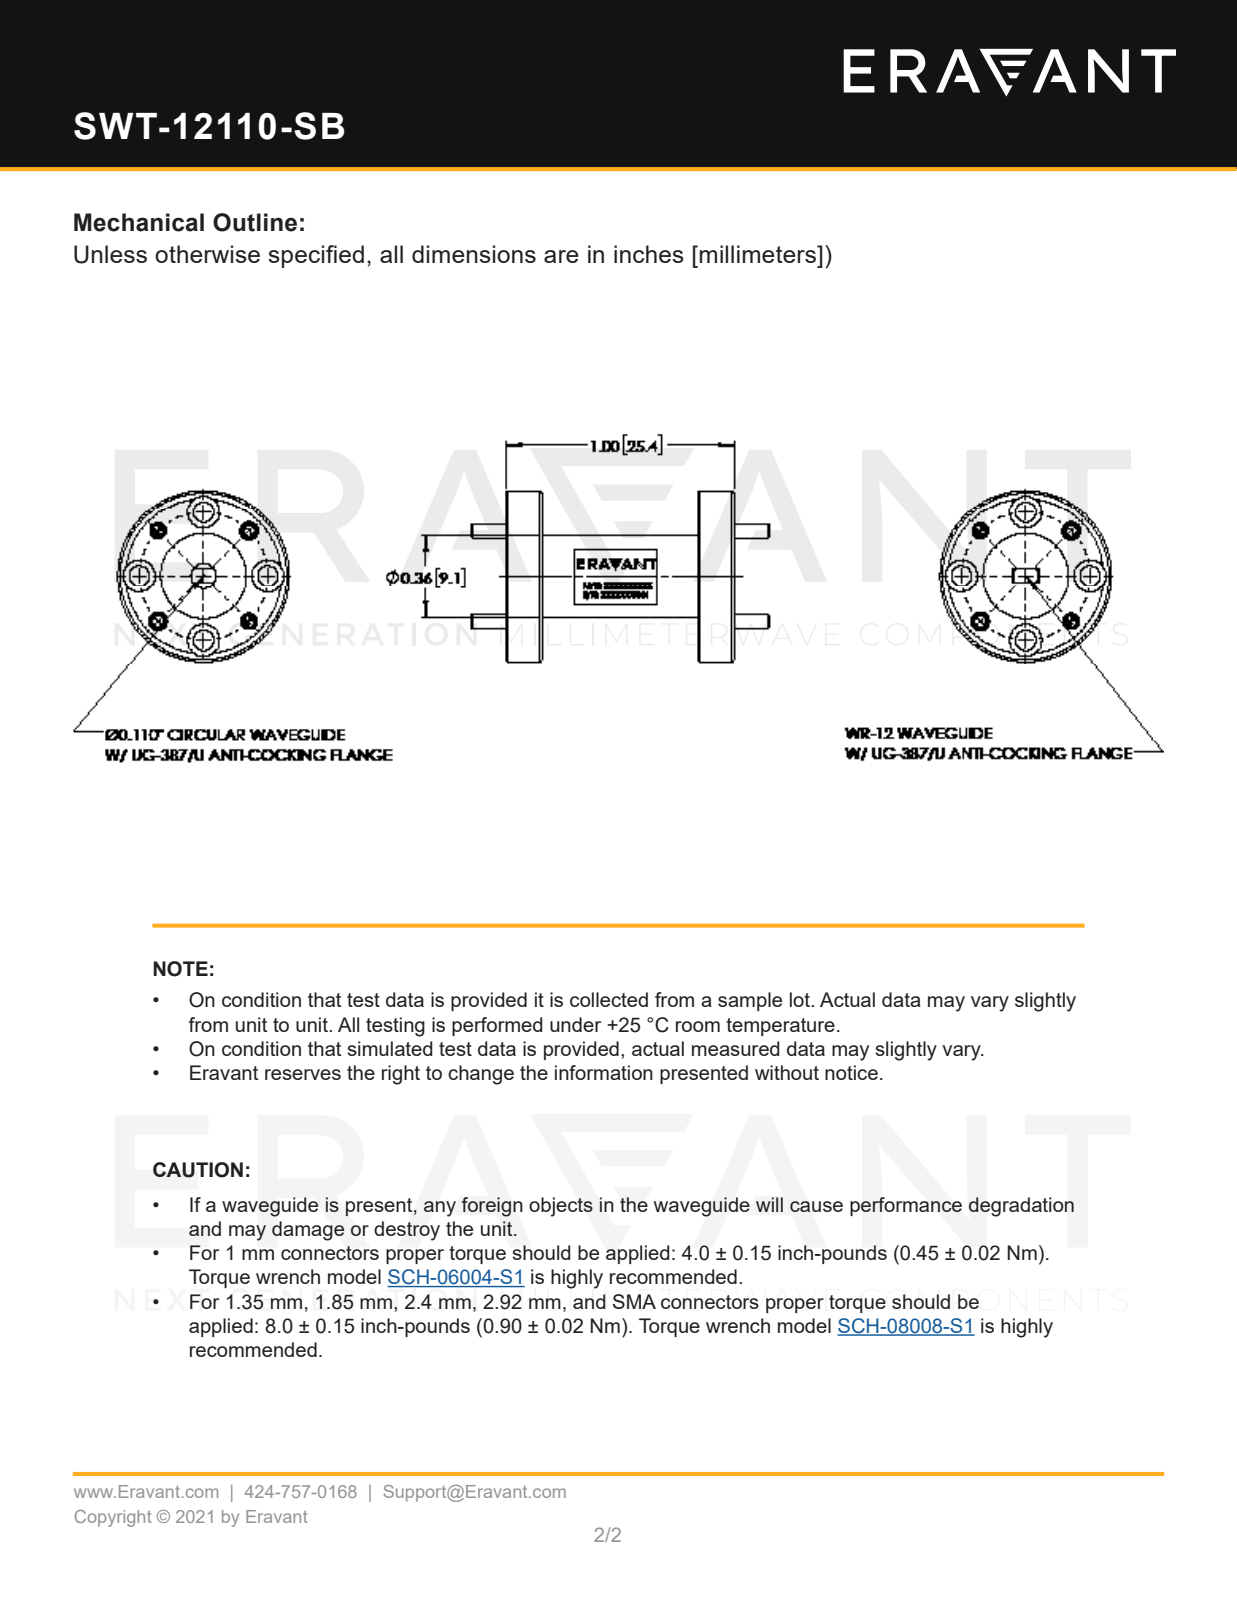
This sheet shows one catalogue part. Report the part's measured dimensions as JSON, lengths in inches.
{"part_name": "SWT-12110-SB", "step_written_by": "SolidWorks 2021 (CONFIG_CONTROL_DESIGN)", "units": "inches", "bodies": {"solids": 5, "faces": 138, "planar": 24, "cylindrical": 66, "other": 48}, "overall_size": [1.305, 0.75, 0.75], "volume_in3": 0.183, "surface_area_in2": 3.601, "round_holes": [[0.061, 4], [0.067, 4], [0.089, 4], [0.14, 4]], "round_bosses_or_shafts": [[0.063, 4], [0.75, 1], [0.375, 1], [0.36, 1]], "face_to_face_distances": [0.13, 0.81, 0.68, 0.94, 0.03, 0.16, 0.84, 0.97, 1, 0.02], "hole_center_spacings": [0.215, 0.398, 0.519, 0.562]}
